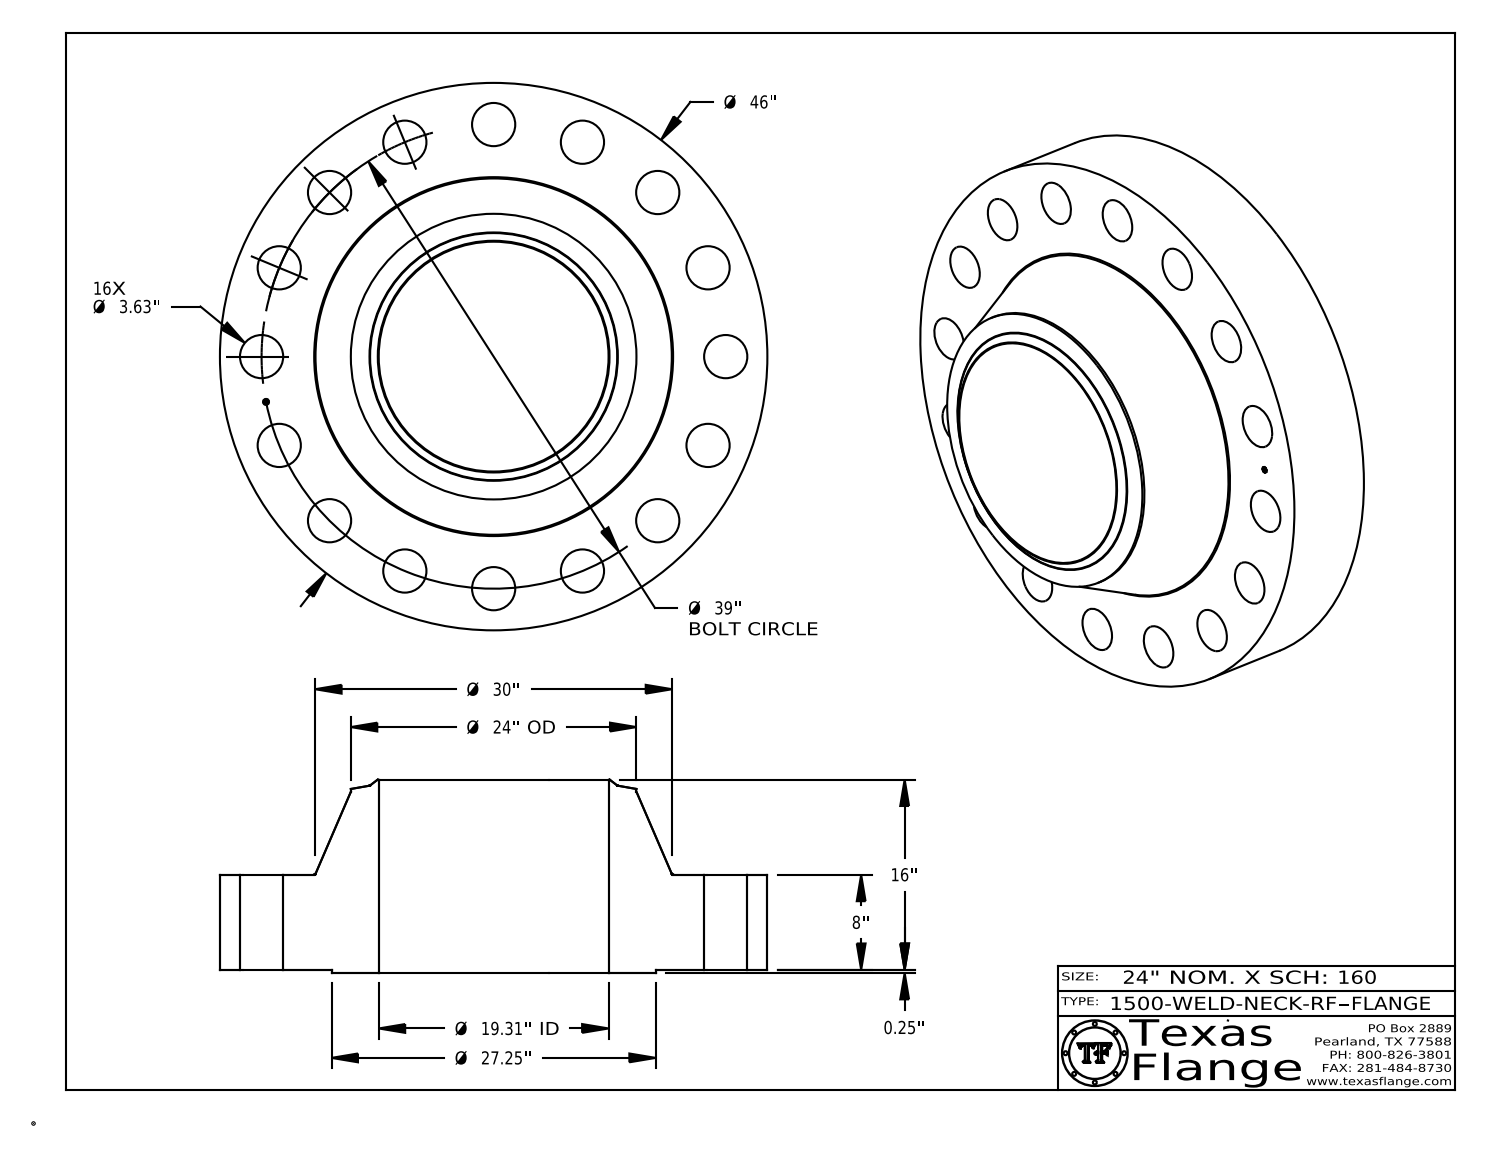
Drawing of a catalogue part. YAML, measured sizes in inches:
part_name: "1500-WELD-NECK-RF"
step_written_by: "CATIA V5 STEP AP214 (AUTOMOTIVE_DESIGN)"
units: inches
bodies: {solids: 1, faces: 439, planar: 369, cylindrical: 60, other: 10}
overall_size: [46, 46, 16.25]
volume: 11745
surface_area: 6448
round_holes:
  - {diameter: 3.63, count: 16}
  - {diameter: 0.495, count: 1}
  - {diameter: 19.312, count: 1}
round_bosses_or_shafts:
  - {diameter: 0.03, count: 8}
  - {diameter: 46, count: 1}
  - {diameter: 27.25, count: 1}
  - {diameter: 24, count: 1}
  - {diameter: 0.39, count: 1}
face_to_face_distances: [8, 0.25, 8.25, 16.25, 16, 8.235, 7.985, 0.015, 8.015, 0.148]
hole_center_spacings: [19.5, 21.667, 27.577, 38.251, 14.925, 36.031, 7.608, 7.609]
